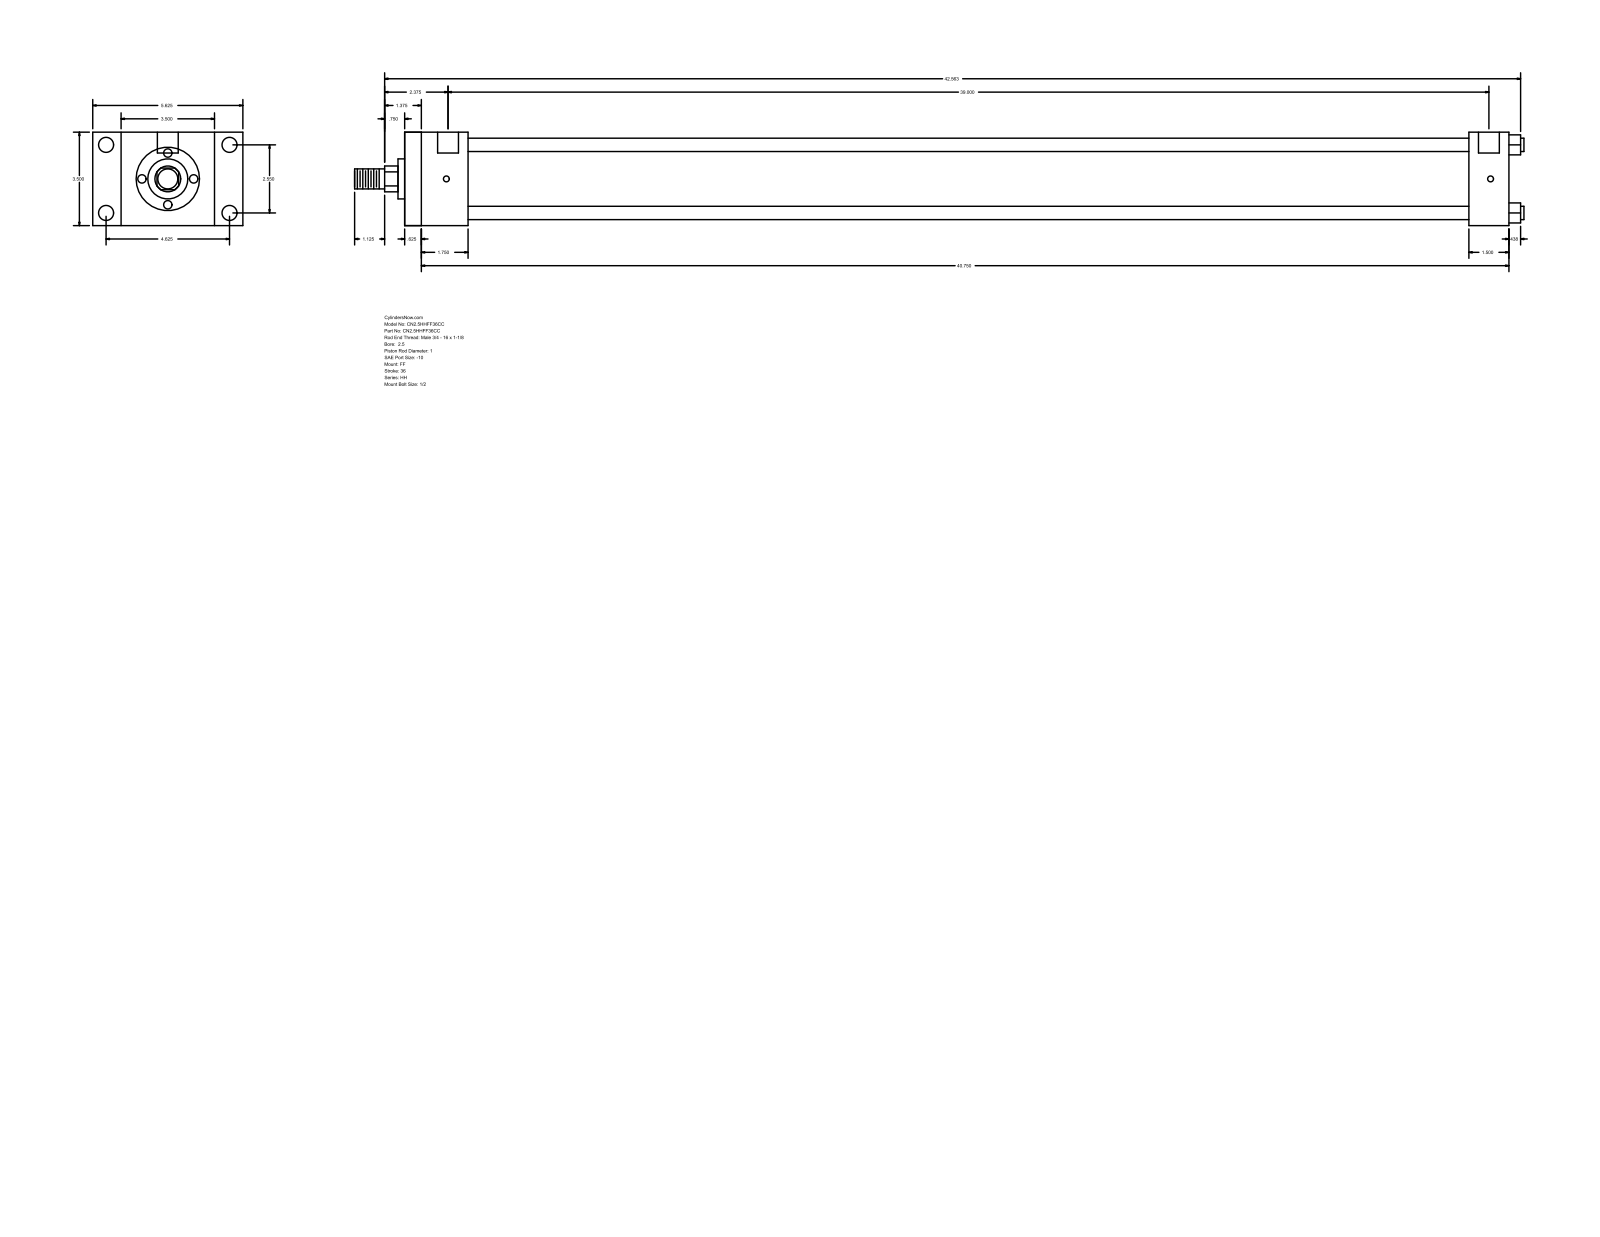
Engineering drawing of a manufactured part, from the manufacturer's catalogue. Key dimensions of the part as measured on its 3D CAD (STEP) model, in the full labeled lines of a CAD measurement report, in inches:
Part name (STEP PRODUCT): HH_FF__0250_1
STEP written by: GSSL Pune (CONFIG_CONTROL_DESIGN)
Units: inches
Bodies: 0 solids, 92 faces (64 planar, 28 cylindrical, 0 other)
Overall size (bounding box): 43.813 × 5.625 × 3.5
Round holes (diameter × count): ⌀0.219 ×4, ⌀0.563 ×4, ⌀0.781 ×2
Round bosses / shafts (diameter × count): ⌀0.5 ×4, ⌀2.875 ×1, ⌀1.5 ×1, ⌀1 ×1, ⌀0.75 ×1
Partial cylindrical surfaces — rounded edges, fillets, slot ends (radius × count): R0.484 ×1
Main face-to-face distances: 3.5, 41.375, 0.625, 40.75, 2.375, 1.75, 39, 39.875, 39.25, 37.5
Hole centre spacings: 0.063, 2.55, 4.625, 5.281, 39.062, 39.125, 39
